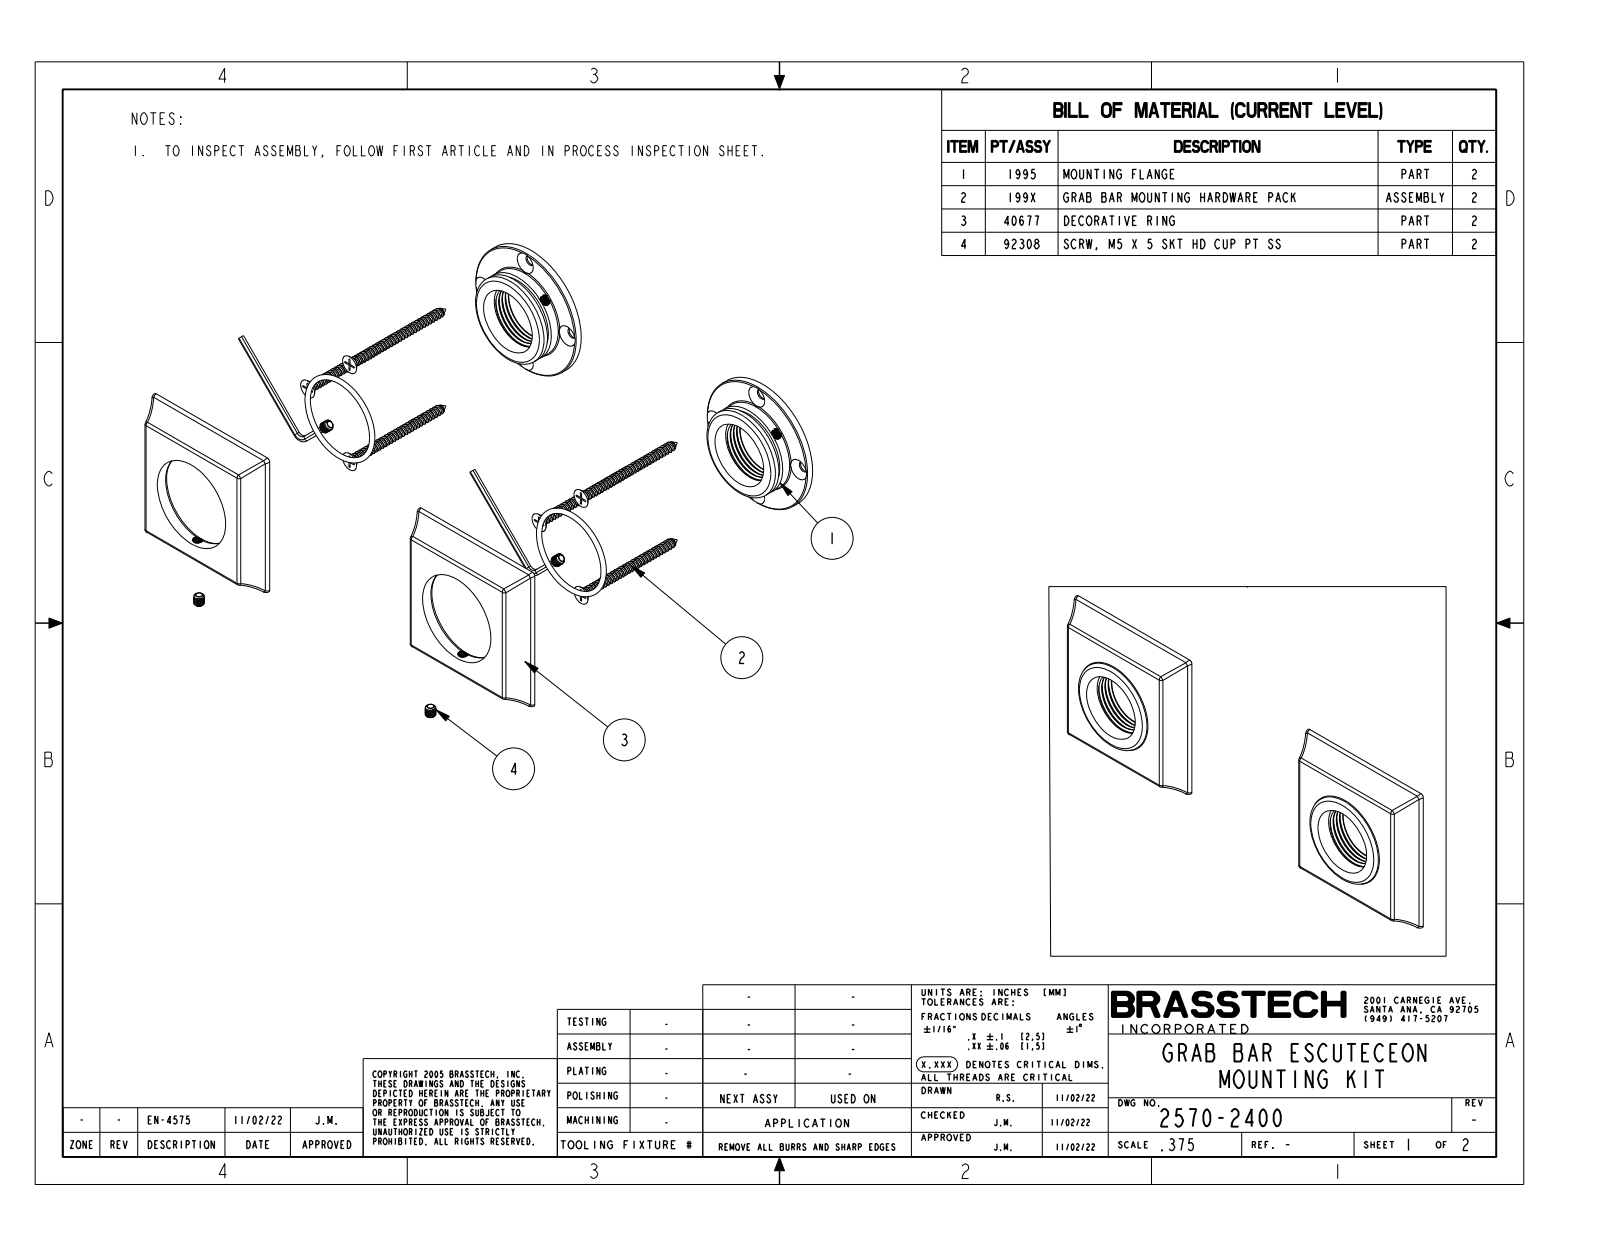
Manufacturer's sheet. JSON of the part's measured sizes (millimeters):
{"part_name": "1995; 40677; 92308; 2570-2400_ASM", "step_written_by": "CREO PARAMETRIC BY PTC INC, 2019352 (CONFIG_CONTROL_DESIGN)", "units": "millimeters", "bodies": {"solids": 6, "faces": 546, "planar": 56, "cylindrical": 232, "other": 258}, "overall_size": [228.6, 76.2, 15.2], "volume_mm3": 84260, "surface_area_mm2": 64580, "round_holes": [[5.1, 8], [4.1, 2], [4.2, 2], [5, 2], [5.2, 2], [29.5, 2], [32, 2], [45, 2]], "round_bosses_or_shafts": [[66, 2], [49, 2], [44.5, 2], [40.5, 2], [5, 2], [5, 2]], "partial_cylinders_radius": [[5.4, 8], [1.5, 6], [3.2, 6], [34.3, 6], [1.3, 4], [2.5, 4]], "face_to_face_distances": [13.3, 3.8, 9.5, 11.4, 15.2, 1.9, 2.5, 5.1, 6.4, 8.9], "hole_center_spacings": [27.6, 39.1, 152.4, 55.2, 127.8, 154.9, 182.1, 124.8]}
